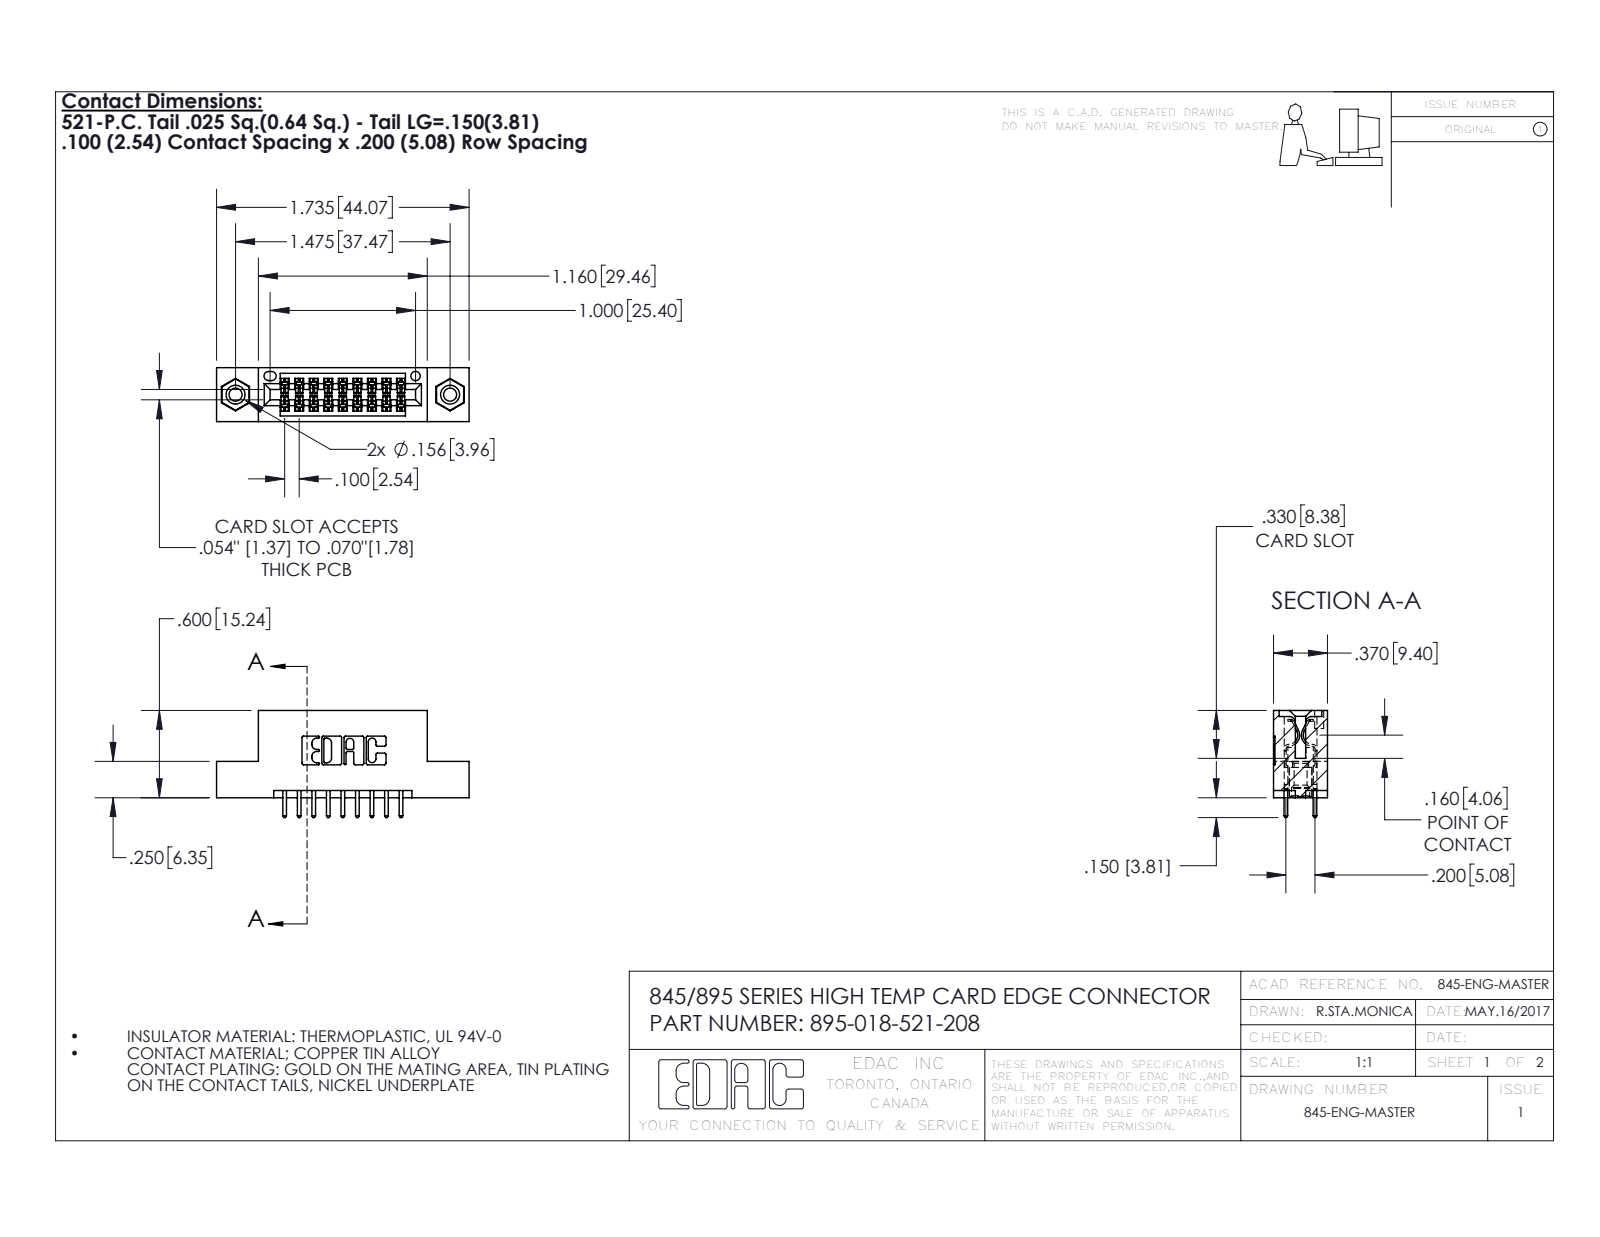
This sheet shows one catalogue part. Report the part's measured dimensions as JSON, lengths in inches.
{"part_name": "345-292-001_345-293-121; 345 Part_Flush Mounting Lugs - 0.156 Dia-TI; 345-250-001_345-250-003-102; 395-018-521-208", "step_written_by": "SolidWorks 2016 (CONFIG_CONTROL_DESIGN)", "units": "inches", "bodies": {"solids": 21, "faces": 1086, "planar": 706, "cylindrical": 364, "other": 16}, "overall_size": [1.735, 0.737, 0.37], "volume_in3": 0.242, "surface_area_in2": 8.031, "round_holes": [[0.089, 2], [0.125, 2], [0.156, 2], [0.064, 1]], "round_bosses_or_shafts": [[0.155, 2]], "partial_cylinders_radius": [[0.006, 27], [0.01, 22], [0.01, 18], [0.007, 6], [0.031, 6], [0.026, 3], [0.014, 2], [0.019, 2]], "face_to_face_distances": [0.2, 0.072, 0.298, 0.37, 0.1, 0.098, 0.272, 0.025, 0.225, 0.6], "hole_center_spacings": [0.27, 1.244, 1.475]}
